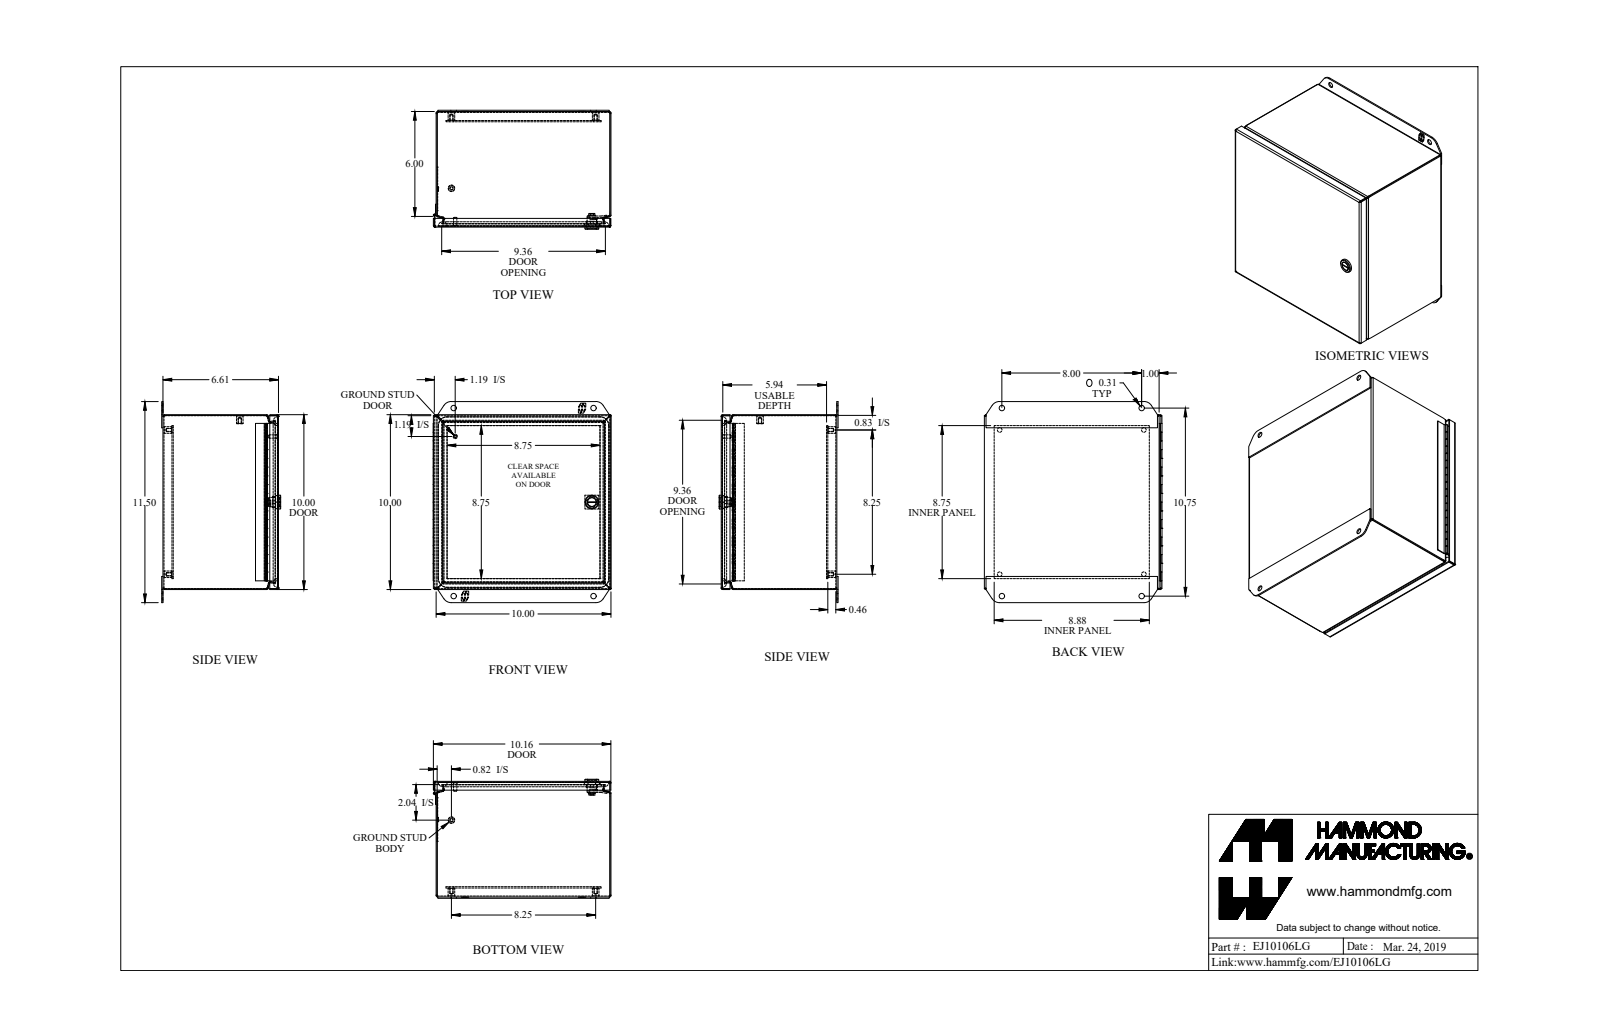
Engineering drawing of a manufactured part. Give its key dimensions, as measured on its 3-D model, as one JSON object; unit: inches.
{"part_name": "EJ10106LG_Default", "step_written_by": "SolidWorks 2019 (CONFIG_CONTROL_DESIGN)", "units": "inches", "bodies": {"solids": 16, "faces": 675, "planar": 377, "cylindrical": 206, "other": 92}, "overall_size": [11.5, 10.165, 6.805], "volume_in3": 39.42, "surface_area_in2": 1304, "round_holes": [[0.156, 5], [0.265, 4], [0.313, 4], [0.05, 1], [0.516, 1]], "round_bosses_or_shafts": [[0.375, 5], [0.788, 1], [0.535, 1], [0.496, 1], [0.435, 1], [0.25, 1], [0.188, 1], [0.1, 1]], "partial_cylinders_radius": [[0.029, 16], [0.086, 16], [0.281, 10], [0.25, 4], [0.499, 4], [0.5, 4], [0.06, 2], [0.539, 2]], "face_to_face_distances": [0.057, 9.943, 6.554, 10, 9.886, 0.072, 0.589, 6.611, 6.497, 0.46], "hole_center_spacings": [8.25, 1.257, 9.501, 8.22, 12.5, 4.131, 5.376, 8]}
